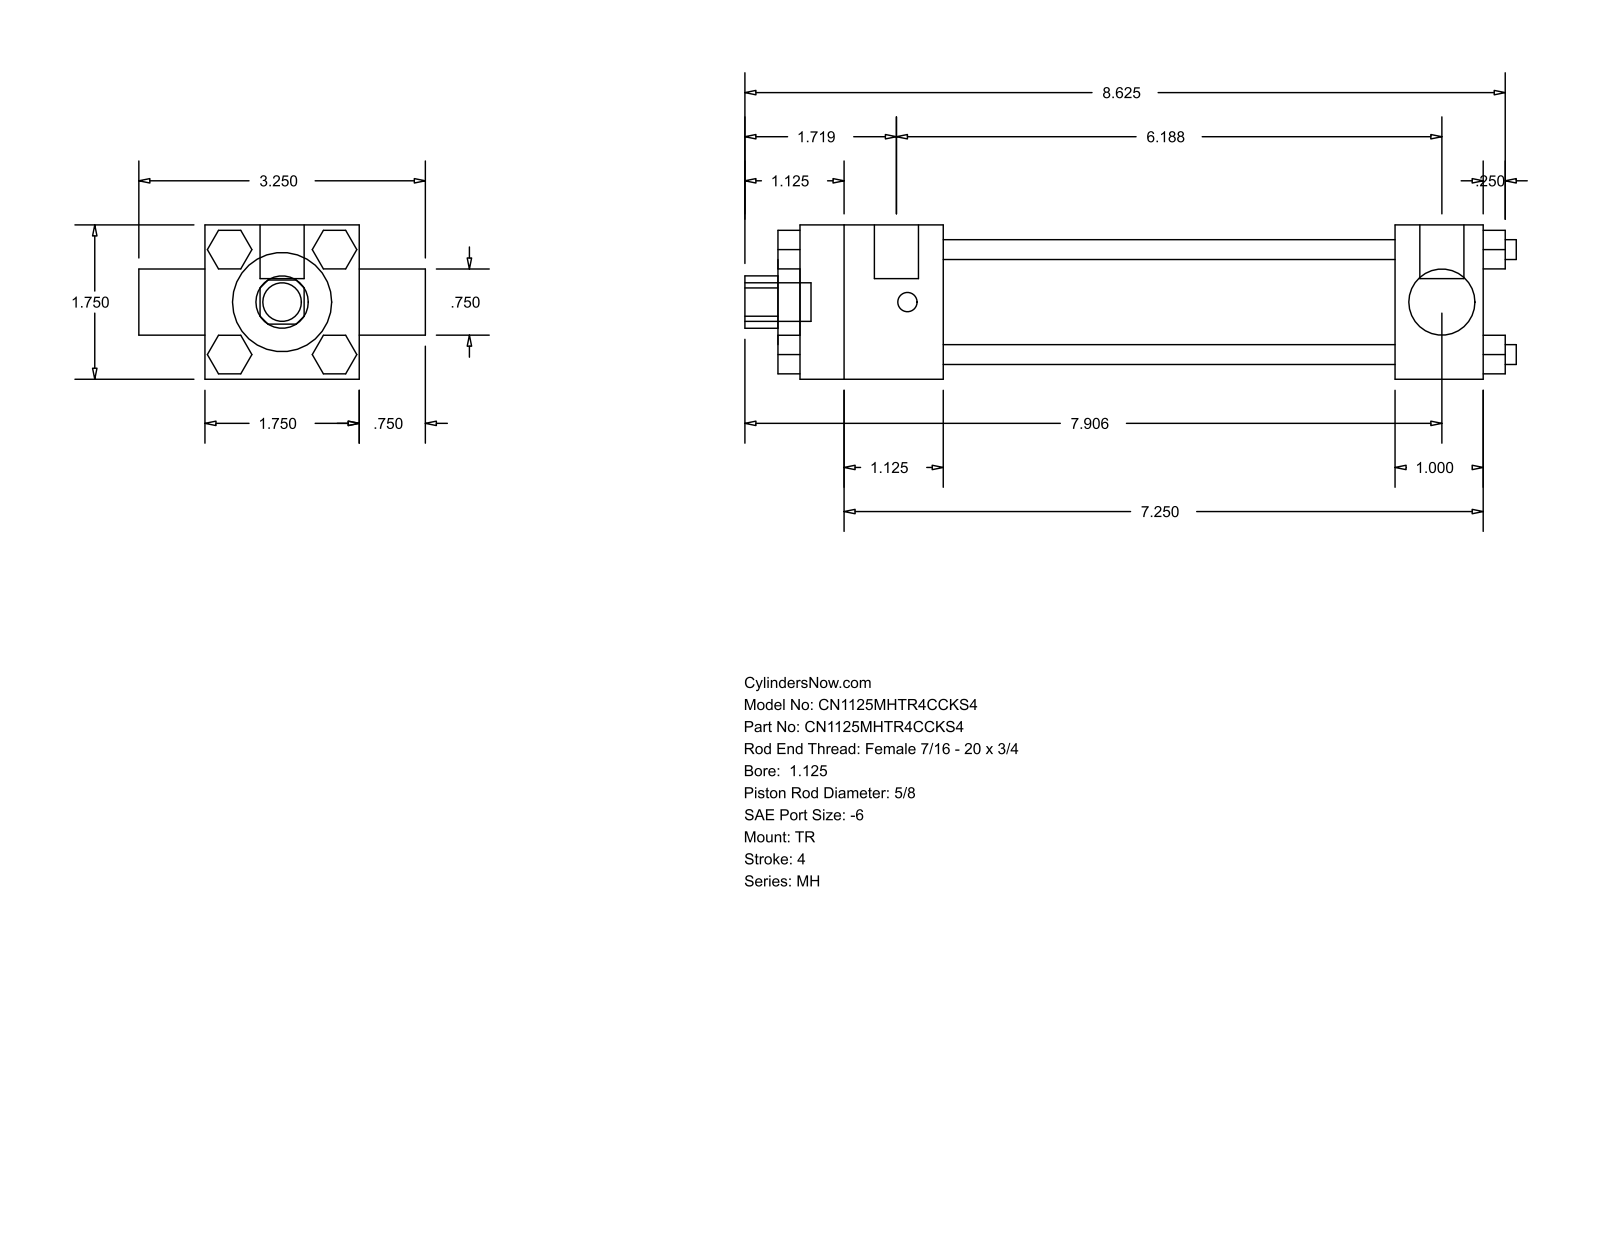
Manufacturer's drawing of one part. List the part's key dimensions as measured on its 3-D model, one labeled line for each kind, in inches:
Part name (STEP PRODUCT): MH_TR__0112_0.625
STEP written by: GSSL Pune (CONFIG_CONTROL_DESIGN)
Units: inches
Bodies: 0 solids, 120 faces (92 planar, 28 cylindrical, 0 other)
Overall size (bounding box): 8.75 × 3.25 × 1.75
Round holes (diameter × count): ⌀0.625 ×1, ⌀0.75 ×1, ⌀1.125 ×1, ⌀1.375 ×1
Round bosses / shafts (diameter × count): ⌀0.225 ×4, ⌀0.219 ×3, ⌀0.5 ×2, ⌀0.437 ×1
Partial cylindrical surfaces — rounded edges, fillets, slot ends (radius × count): R0.297 ×1
Main face-to-face distances: 1.75, 0.25, 8, 0.437, 5.125, 6.125, 1, 1.625, 6.75, 7.75
